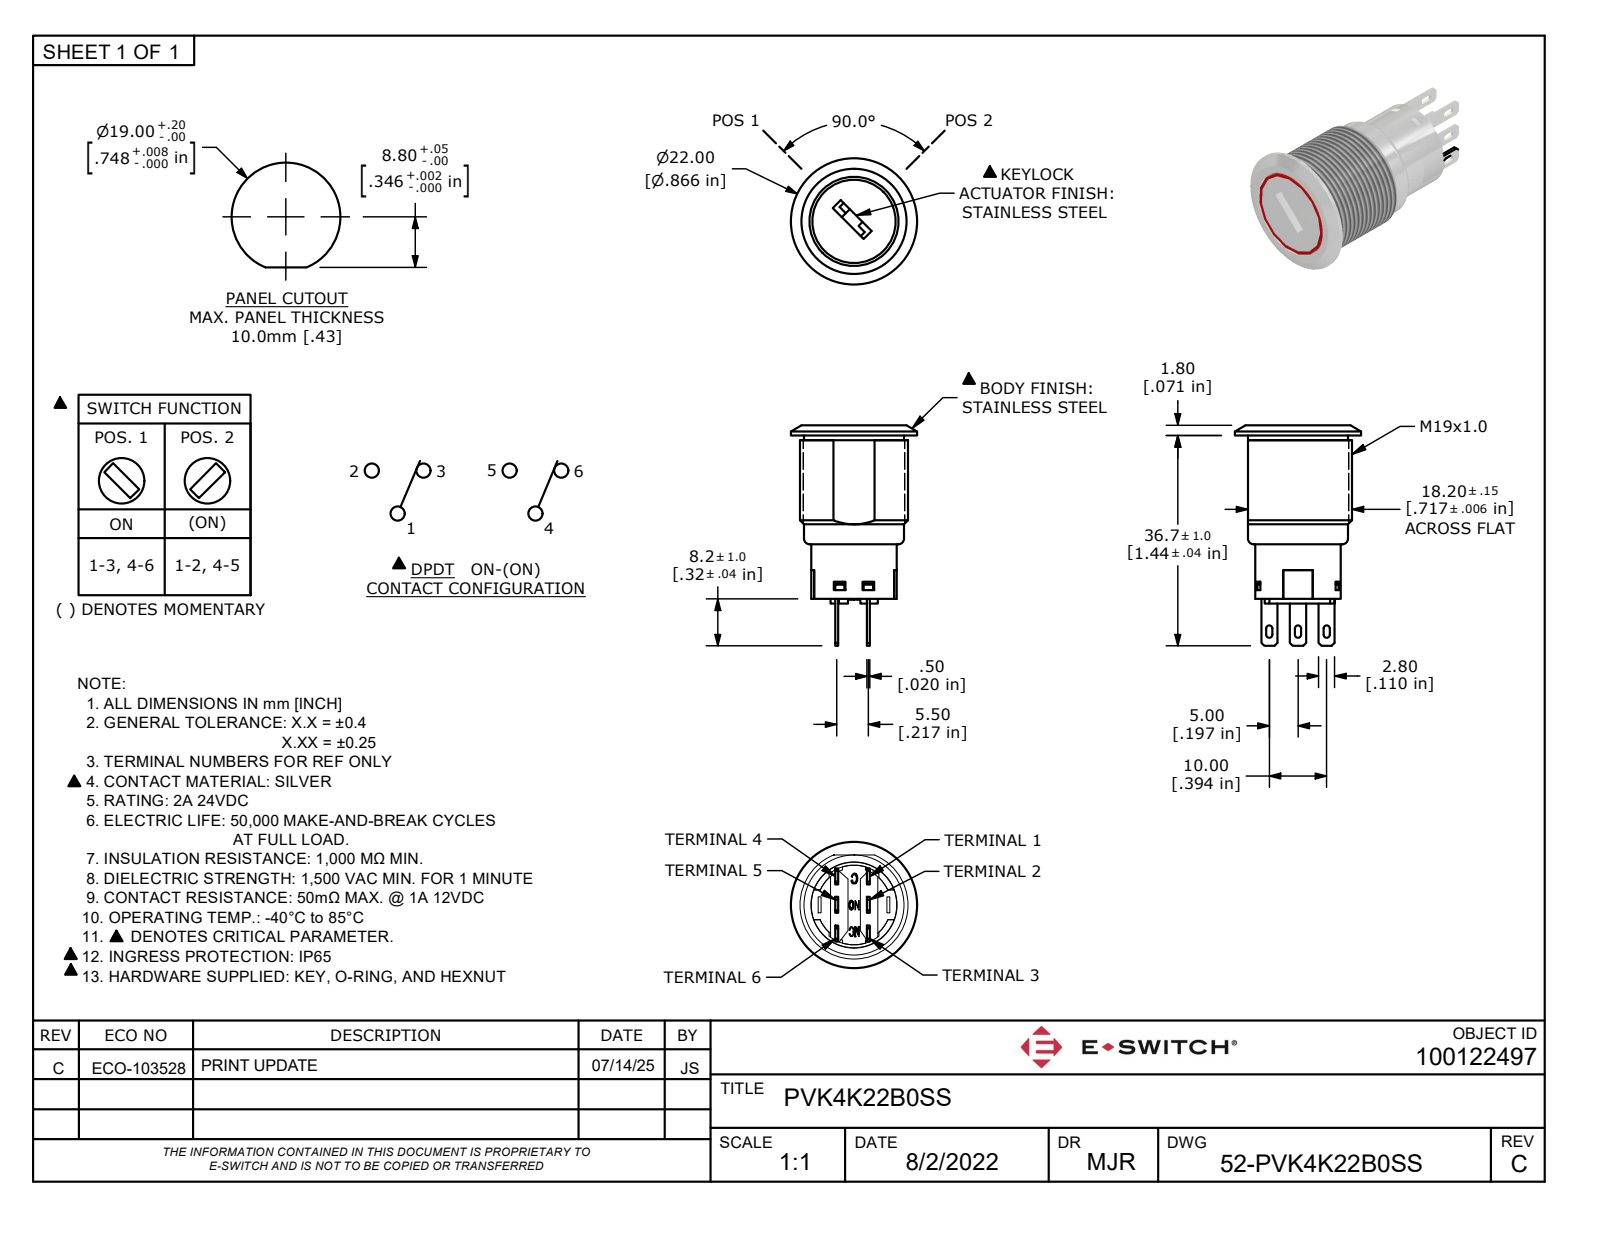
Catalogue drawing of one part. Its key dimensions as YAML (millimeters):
part_name: "PVK4K22xx0SS"
step_written_by: "Autodesk Inventor 2020 (AUTOMOTIVE_DESIGN)"
units: millimeters
bodies: {solids: 2, faces: 277, planar: 202, cylindrical: 39, other: 36}
overall_size: [38.5, 22, 22]
volume: 9414
surface_area: 4028
round_holes:
  - {diameter: 13.7, count: 1}
  - {diameter: 15, count: 1}
  - {diameter: 17.5, count: 1}
  - {diameter: 22, count: 1}
round_bosses_or_shafts:
  - {diameter: 18.9, count: 1}
  - {diameter: 15.8, count: 1}
  - {diameter: 15.5, count: 1}
  - {diameter: 14.9, count: 1}
  - {diameter: 14.5, count: 1}
partial_cylinders:
  - {radius: 0.55, count: 6}
  - {radius: 6.45, count: 1}
  - {radius: 6.95, count: 1}
face_to_face_distances: [0.4, 1.4, 1.8, 15.3, 16.7, 0.5, 5.5, 13.2, 30.3, 29.9]
